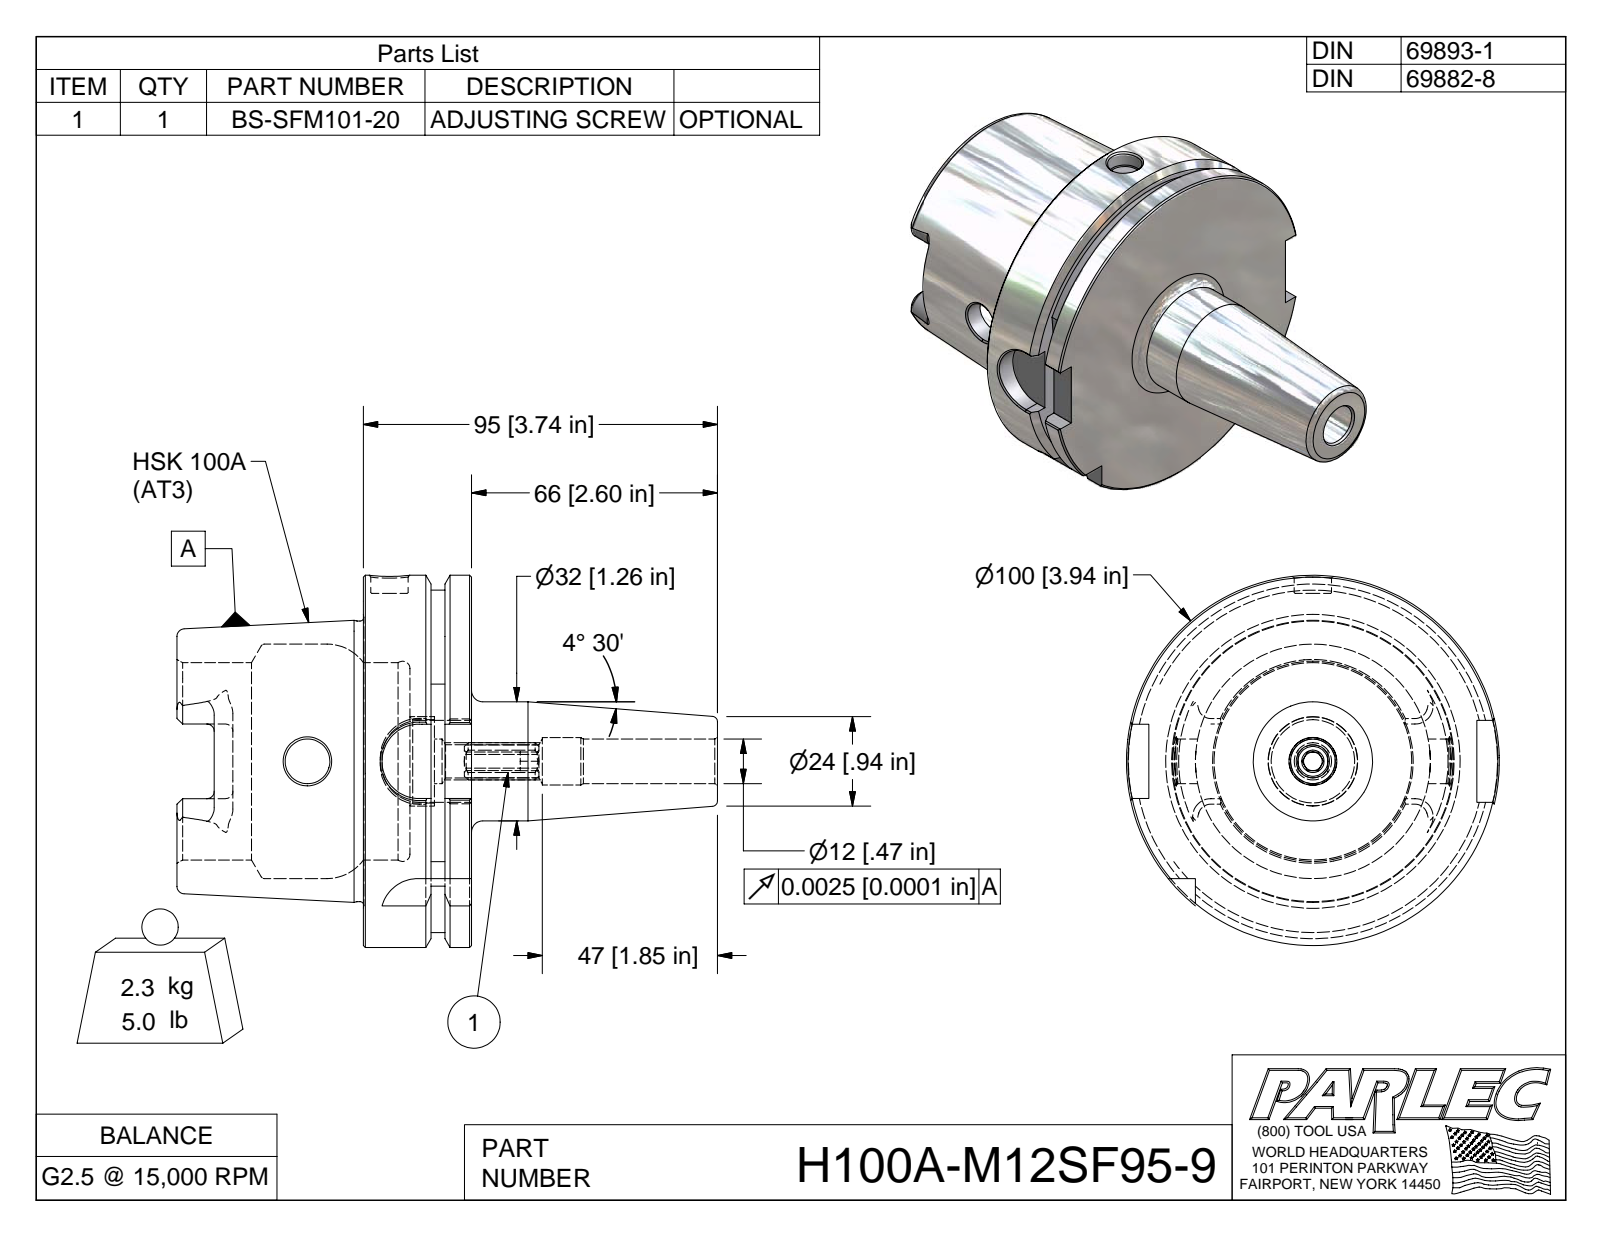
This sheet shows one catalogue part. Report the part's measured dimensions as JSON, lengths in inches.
{"part_name": "H100A-M12SF95-9; H100A-M12SF95-9-1; BS-SFM101-20", "step_written_by": "Autodesk Inventor 2009 (AUTOMOTIVE_DESIGN)", "units": "inches", "bodies": {"solids": 2, "faces": 147, "planar": 48, "cylindrical": 29, "other": 70}, "overall_size": [5.709, 3.937, 3.937], "volume_in3": 18.01, "surface_area_in2": 90.14, "round_holes": [[0.394, 1], [0.471, 1], [0.472, 1], [0.501, 1], [0.881, 1], [2.087, 1], [2.48, 1]], "round_bosses_or_shafts": [[3.937, 1], [2.967, 1], [1.26, 1]], "partial_cylinders_radius": [[0.394, 4], [0.079, 3], [0.192, 2], [0.197, 1], [1.811, 1]], "face_to_face_distances": [1.142, 0.492, 0.65, 1.969, 2.461, 3.11, 2.682, 0.713, 0.221, 0.428]}
